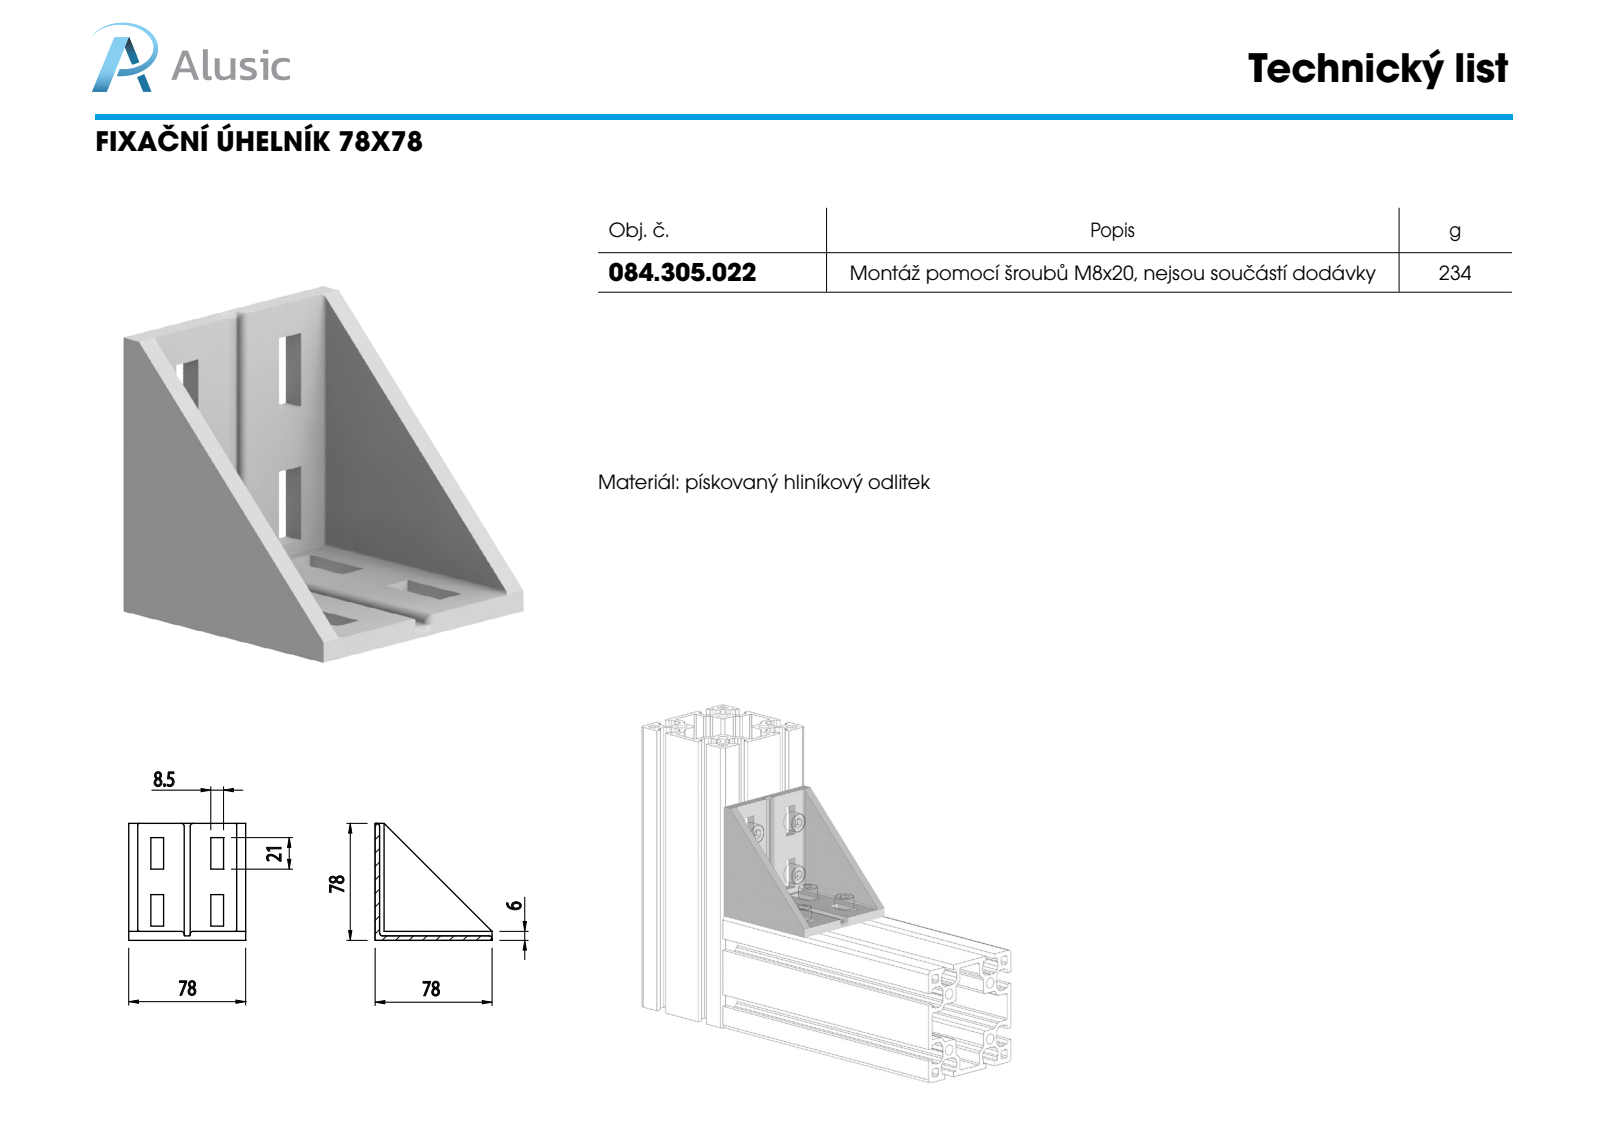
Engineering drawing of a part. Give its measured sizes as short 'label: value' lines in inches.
name: 084.305.022
written by: SolidWorks 2011 (CONFIG_CONTROL_DESIGN)
unit: in
bodies: 1 solid, 75 faces (50 planar, 19 cylindrical, 6 other)
size: 3.071 × 3.071 × 3.071
volume: 5.54 in³; area: 56.42 in²
rounds: 11× R0.079, 4× R0.02, 4× R0.039
face distances: 0.236, 2.835, 3.071, 2.598, 0.581, 2.49, 0.344, 2.254, 0.915, 2.156
